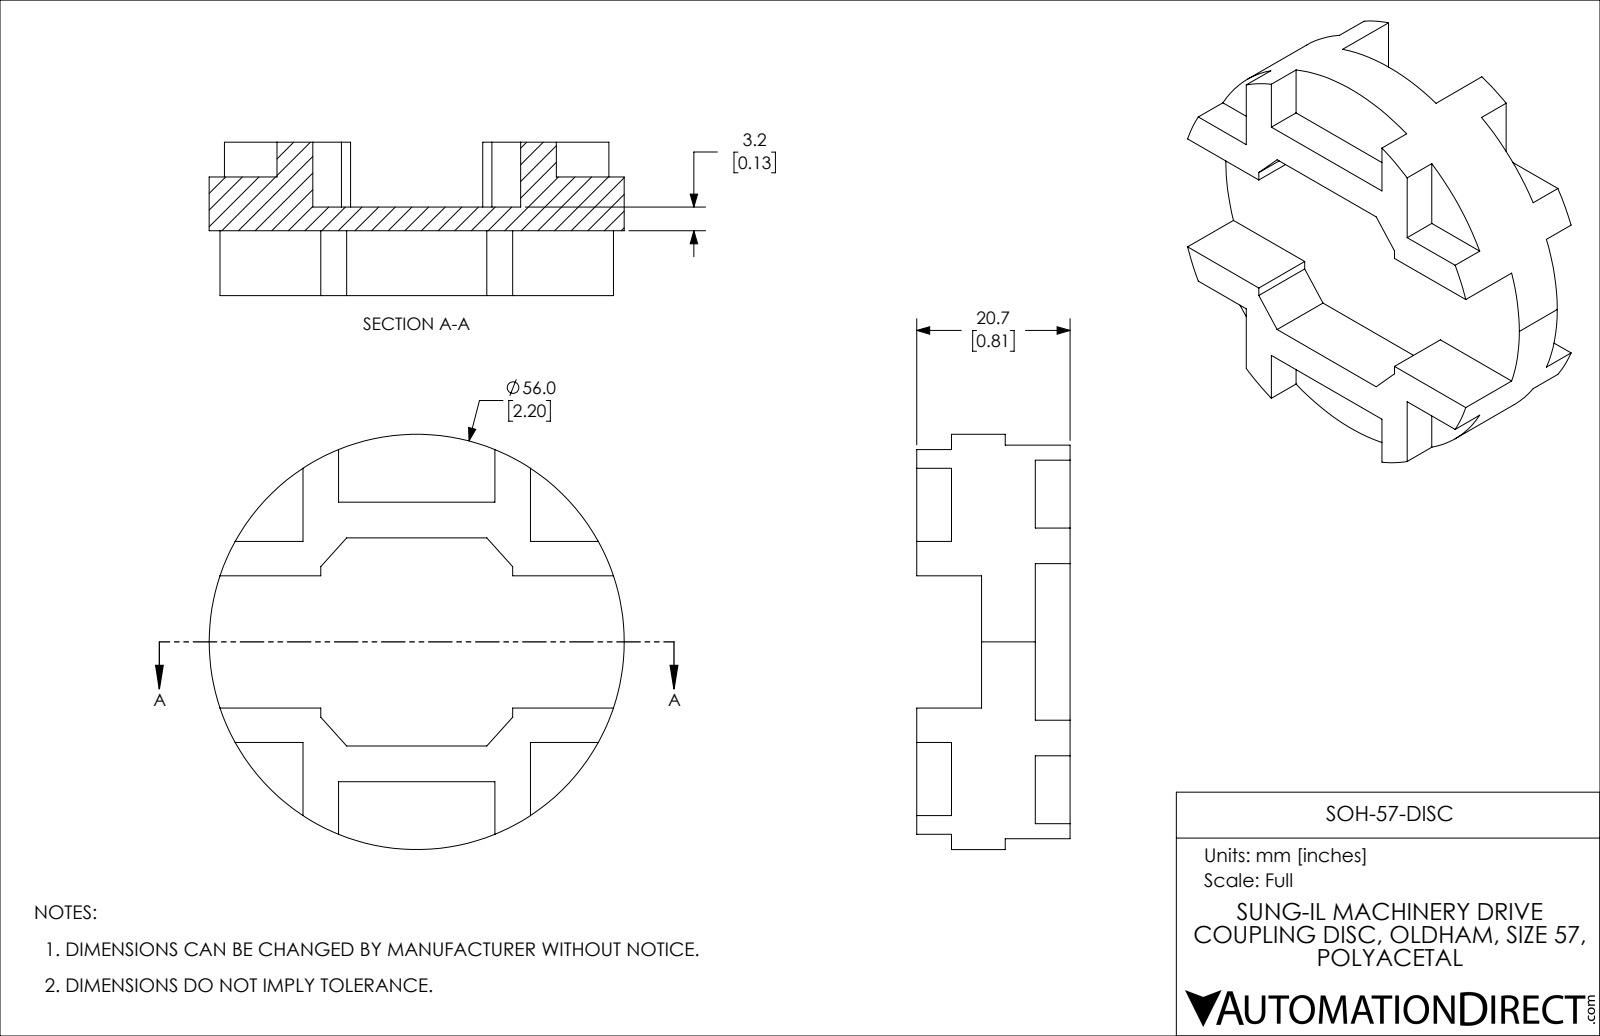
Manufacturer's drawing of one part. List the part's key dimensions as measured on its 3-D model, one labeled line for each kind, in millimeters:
Part name (STEP PRODUCT): SOH-57-DISC
STEP written by: SolidWorks 2021 (CONFIG_CONTROL_DESIGN)
Units: millimetres
Bodies: 1 solid, 76 faces (74 planar, 2 cylindrical, 0 other)
Overall size (bounding box): 56 × 56 × 20.7
Volume: 24 318 mm³ · Surface area: 10 458 mm²
Round bosses / shafts (diameter × count): ⌀56 ×1
Main face-to-face distances: 8.75, 11.95, 3.2, 4.7, 16, 4.05, 7.25, 20.7, 5.11, 22.93
